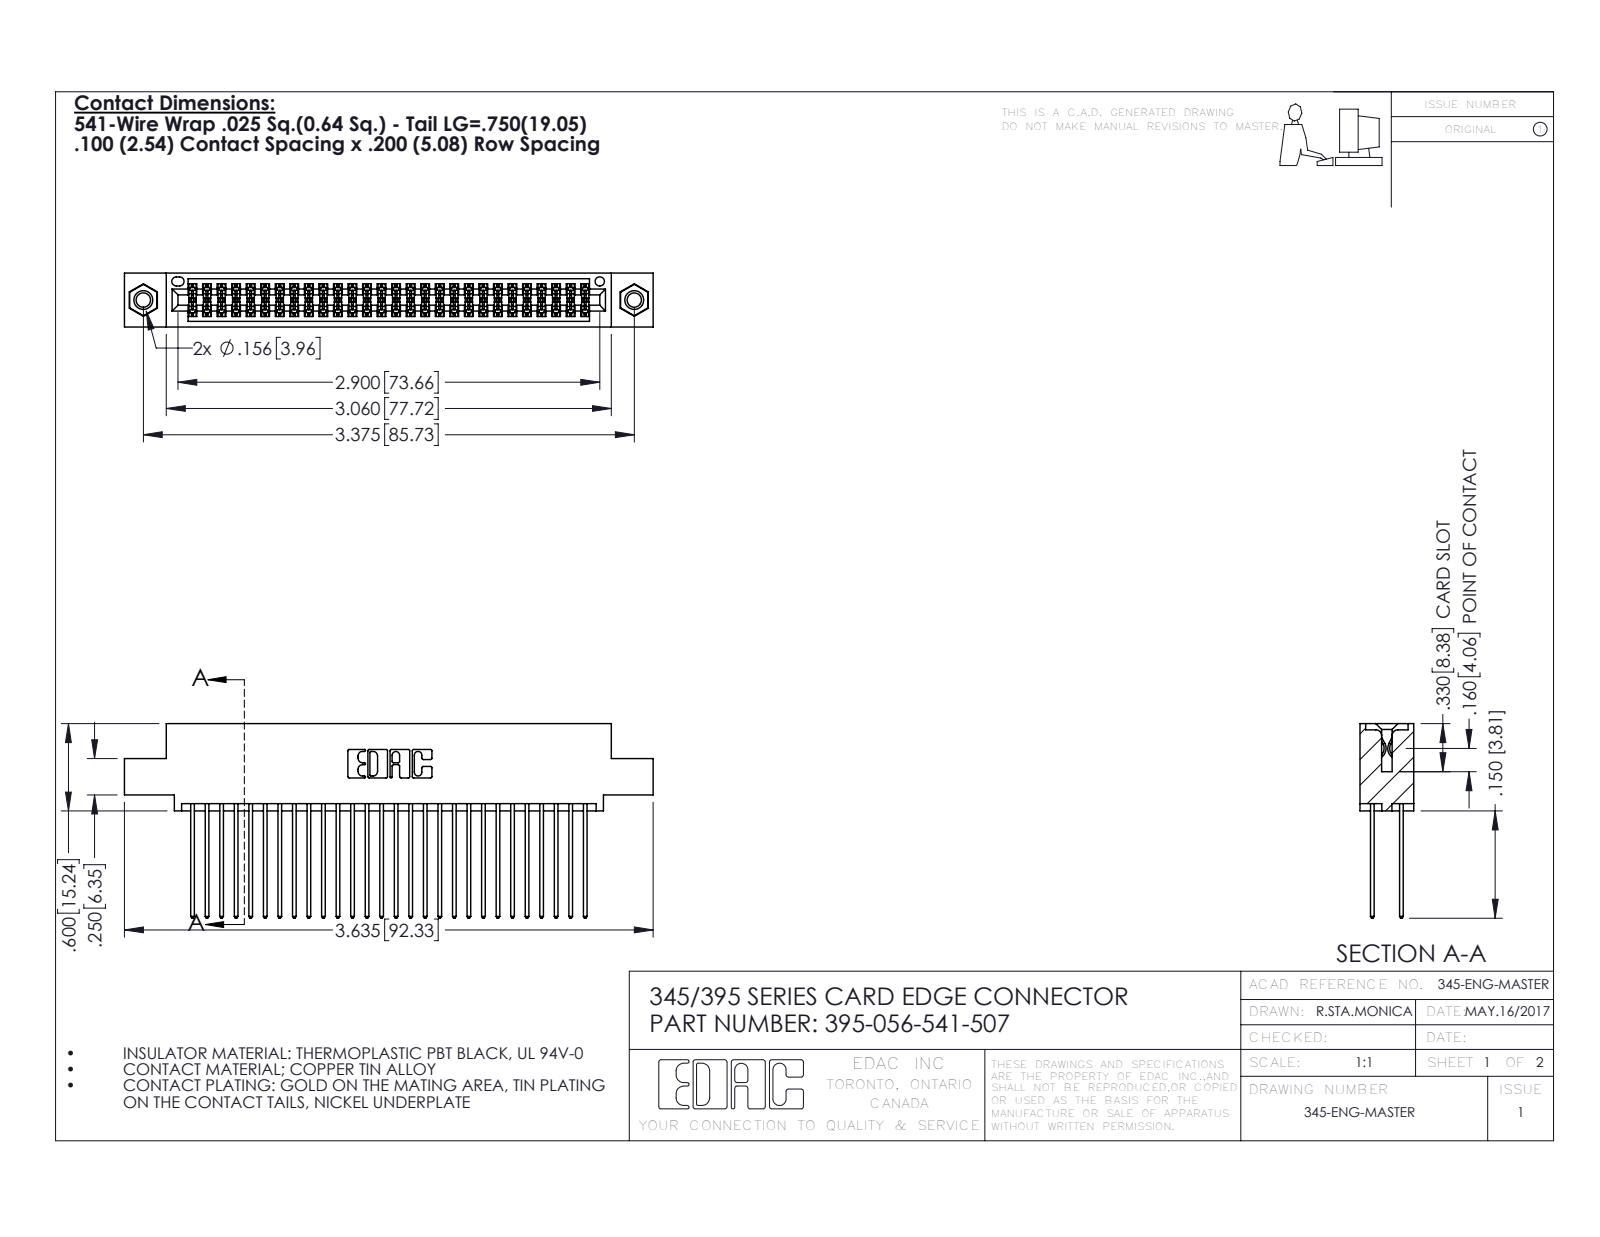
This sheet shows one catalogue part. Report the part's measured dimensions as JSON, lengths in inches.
{"part_name": "395-056-541-507; 345 Part_0.110 Offset - 0.156 Dia-TI; 345-292-001_345-293-141; 345-250-001_345-250-005-103", "step_written_by": "SolidWorks 2016 (CONFIG_CONTROL_DESIGN)", "units": "inches", "bodies": {"solids": 59, "faces": 2990, "planar": 1964, "cylindrical": 1010, "other": 16}, "overall_size": [3.635, 1.337, 0.37], "volume_in3": 0.554, "surface_area_in2": 22.9, "round_holes": [[0.098, 2], [0.125, 2], [0.156, 2], [0.064, 1]], "round_bosses_or_shafts": [[0.155, 2]], "partial_cylinders_radius": [[0.006, 84], [0.01, 56], [0.01, 22], [0.007, 6], [0.031, 6], [0.026, 3], [0.014, 2], [0.019, 2]], "face_to_face_distances": [0.072, 0.298, 0.2, 0.098, 0.272, 0.025, 0.225, 0.37, 0.175, 0.149], "hole_center_spacings": [0.27, 3.14, 3.375]}
